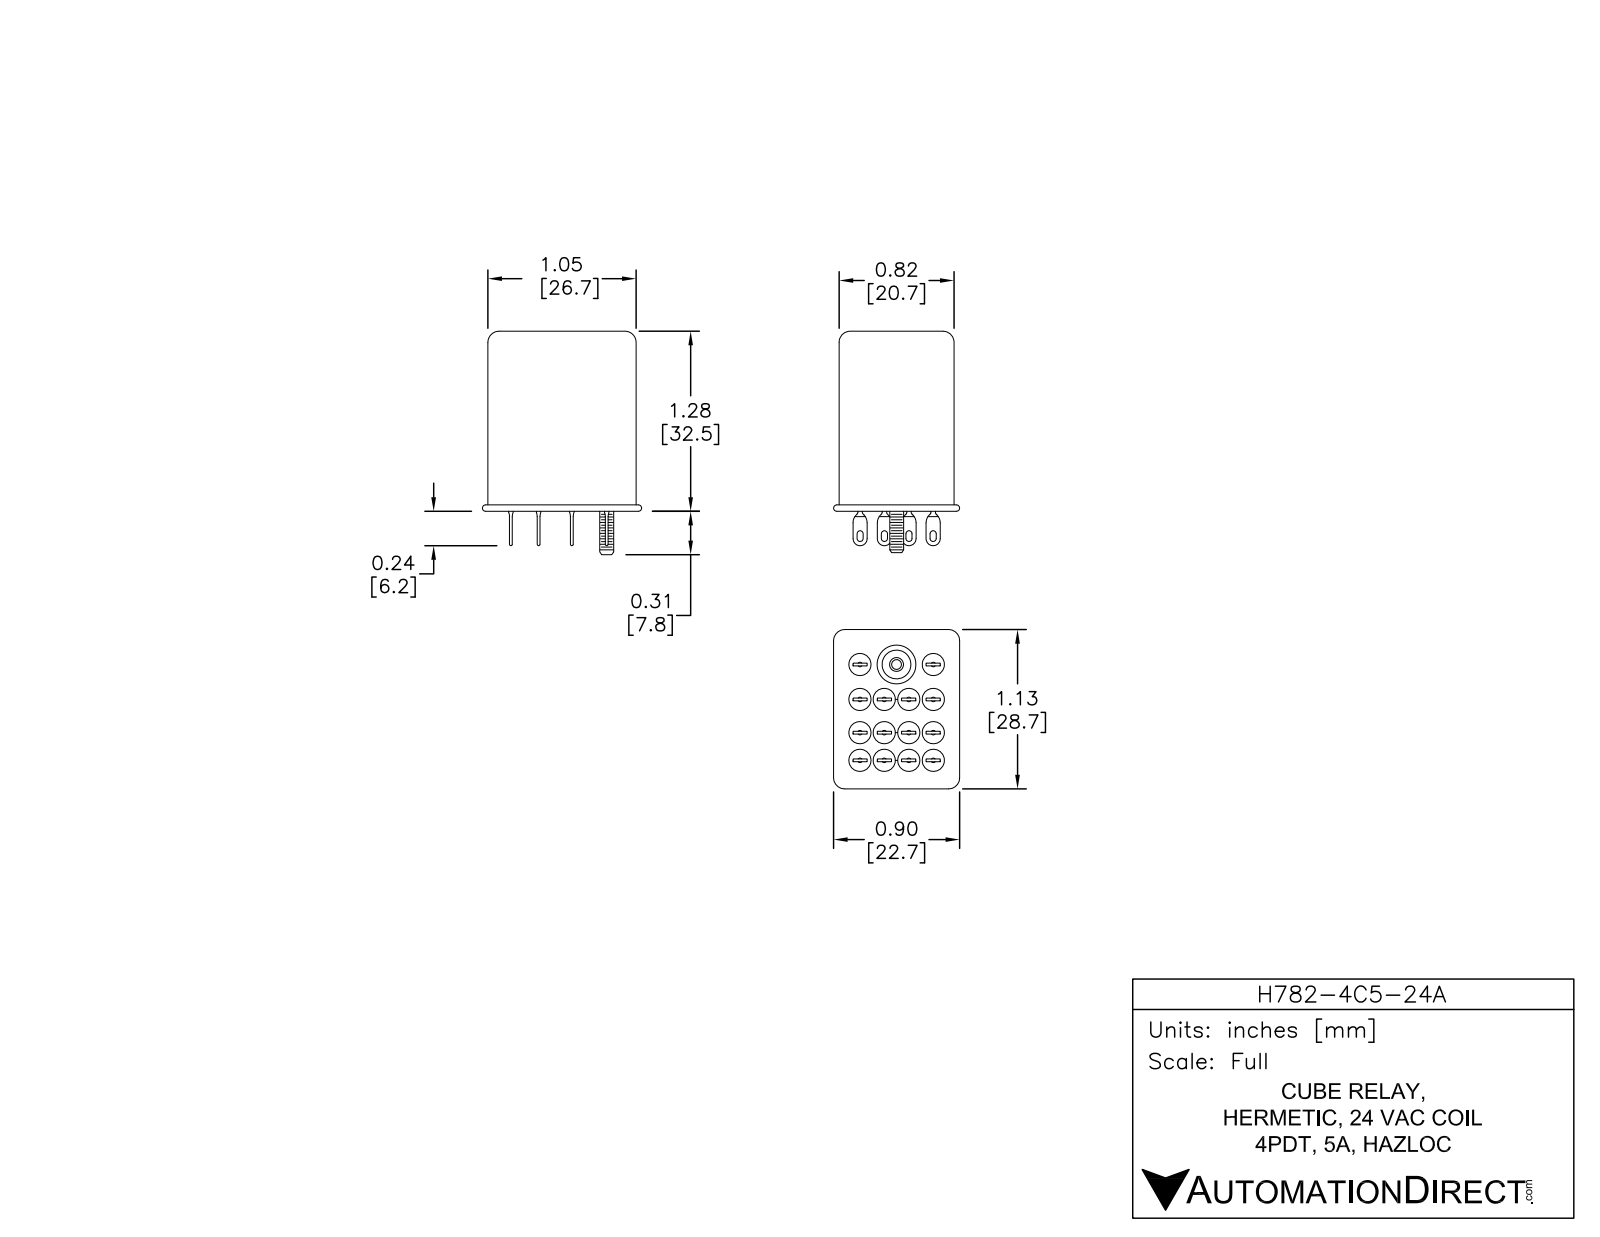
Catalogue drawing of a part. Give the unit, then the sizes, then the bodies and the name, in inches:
Units: inches
Overall size (bounding box): 1.383 × 1.134 × 0.902
Round holes (diameter × count): ⌀0.236 ×1
Round bosses / shafts (diameter × count): ⌀0.124 ×14, ⌀0.094 ×1
Partial cylindrical surfaces — rounded edges, fillets, slot ends (radius × count): R0.004 ×56, R0.02 ×36, R0.008 ×8, R0.079 ×4
Main face-to-face distances: 0.807, 1.087, 1.043, 1.087, 0.205, 0.016, 0.409, 0.394, 0.189, 0.22
Volume: 0.931 in³ · Surface area: 6.406 in²
Bodies: 2 solids, 408 faces (186 planar, 178 cylindrical, 44 other)
Part name (STEP PRODUCT): H782-4C5-24A
STEP written by: SolidWorks 2013 (AUTOMOTIVE_DESIGN)
